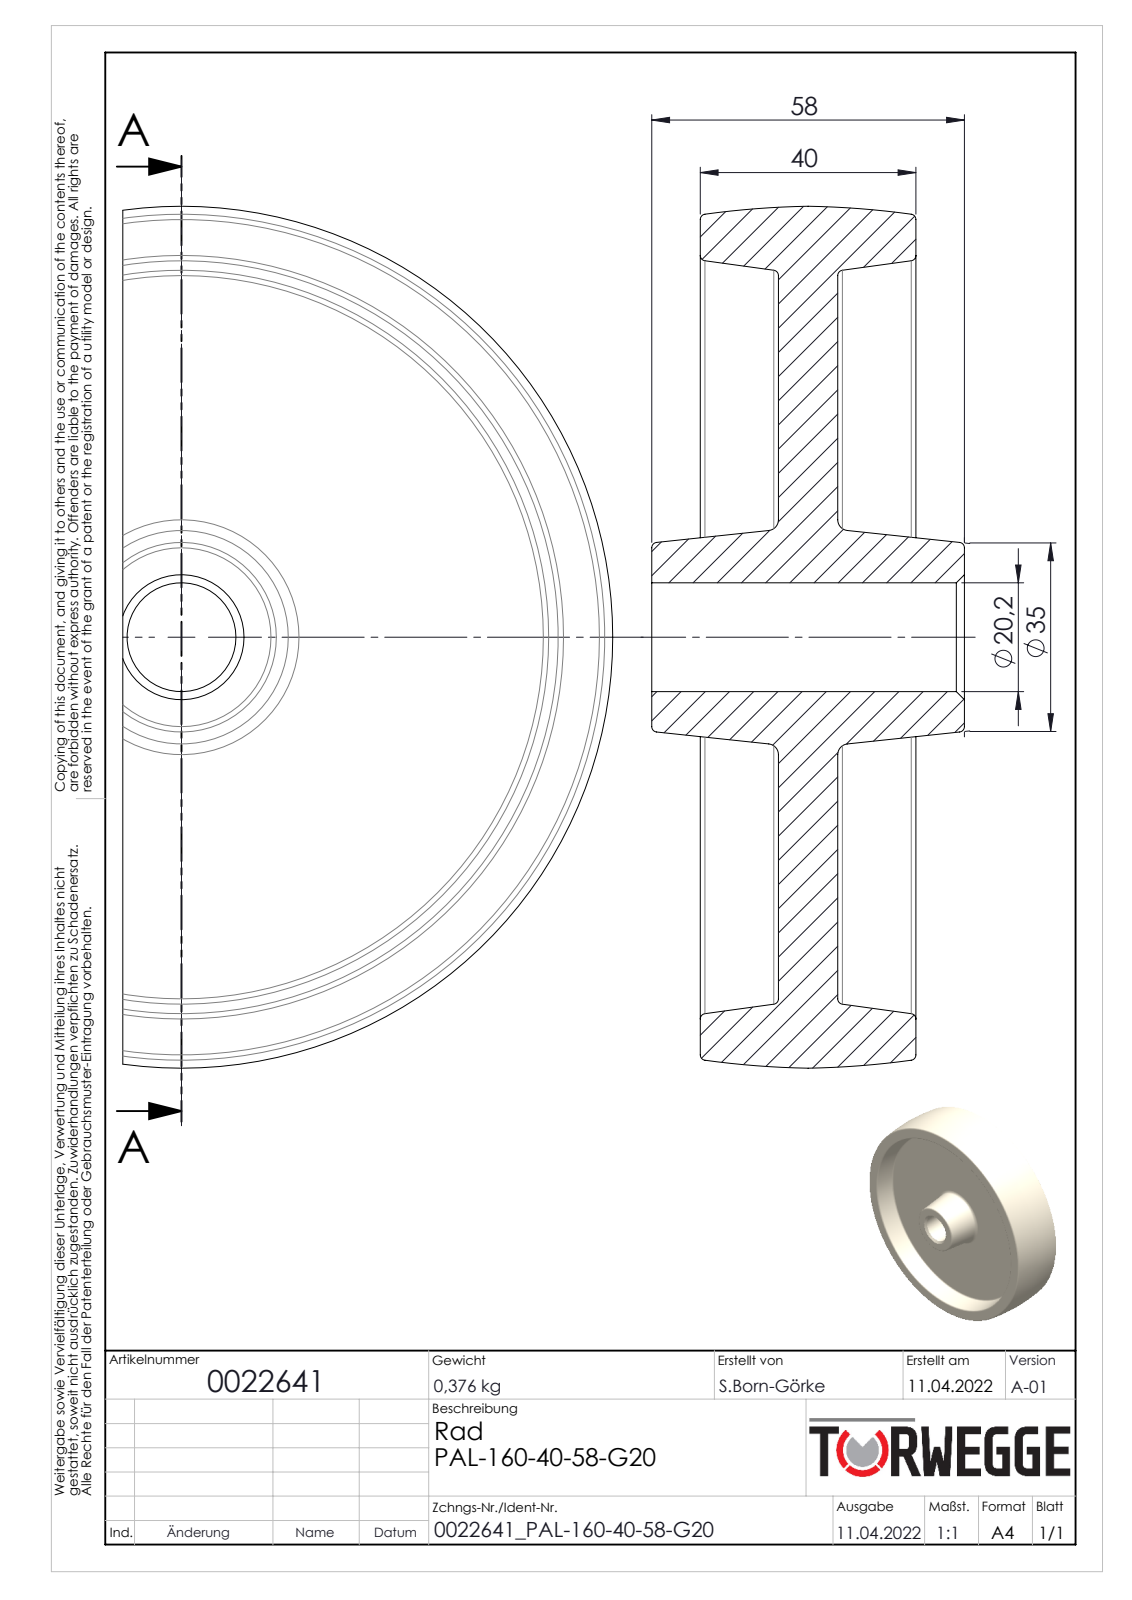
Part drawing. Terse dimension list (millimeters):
name: 0022641
written by: SolidWorks 2020 (AUTOMOTIVE_DESIGN)
unit: mm
bodies: 1 solid, 42 faces (6 planar, 2 cylindrical, 34 other)
size: 160 × 160 × 58
volume: 391 984 mm³; area: 76 500 mm²
holes: 1× ⌀20.2
face distances: 11, 14.5, 25.5, 40, 9, 23.5, 34.5, 49, 58
